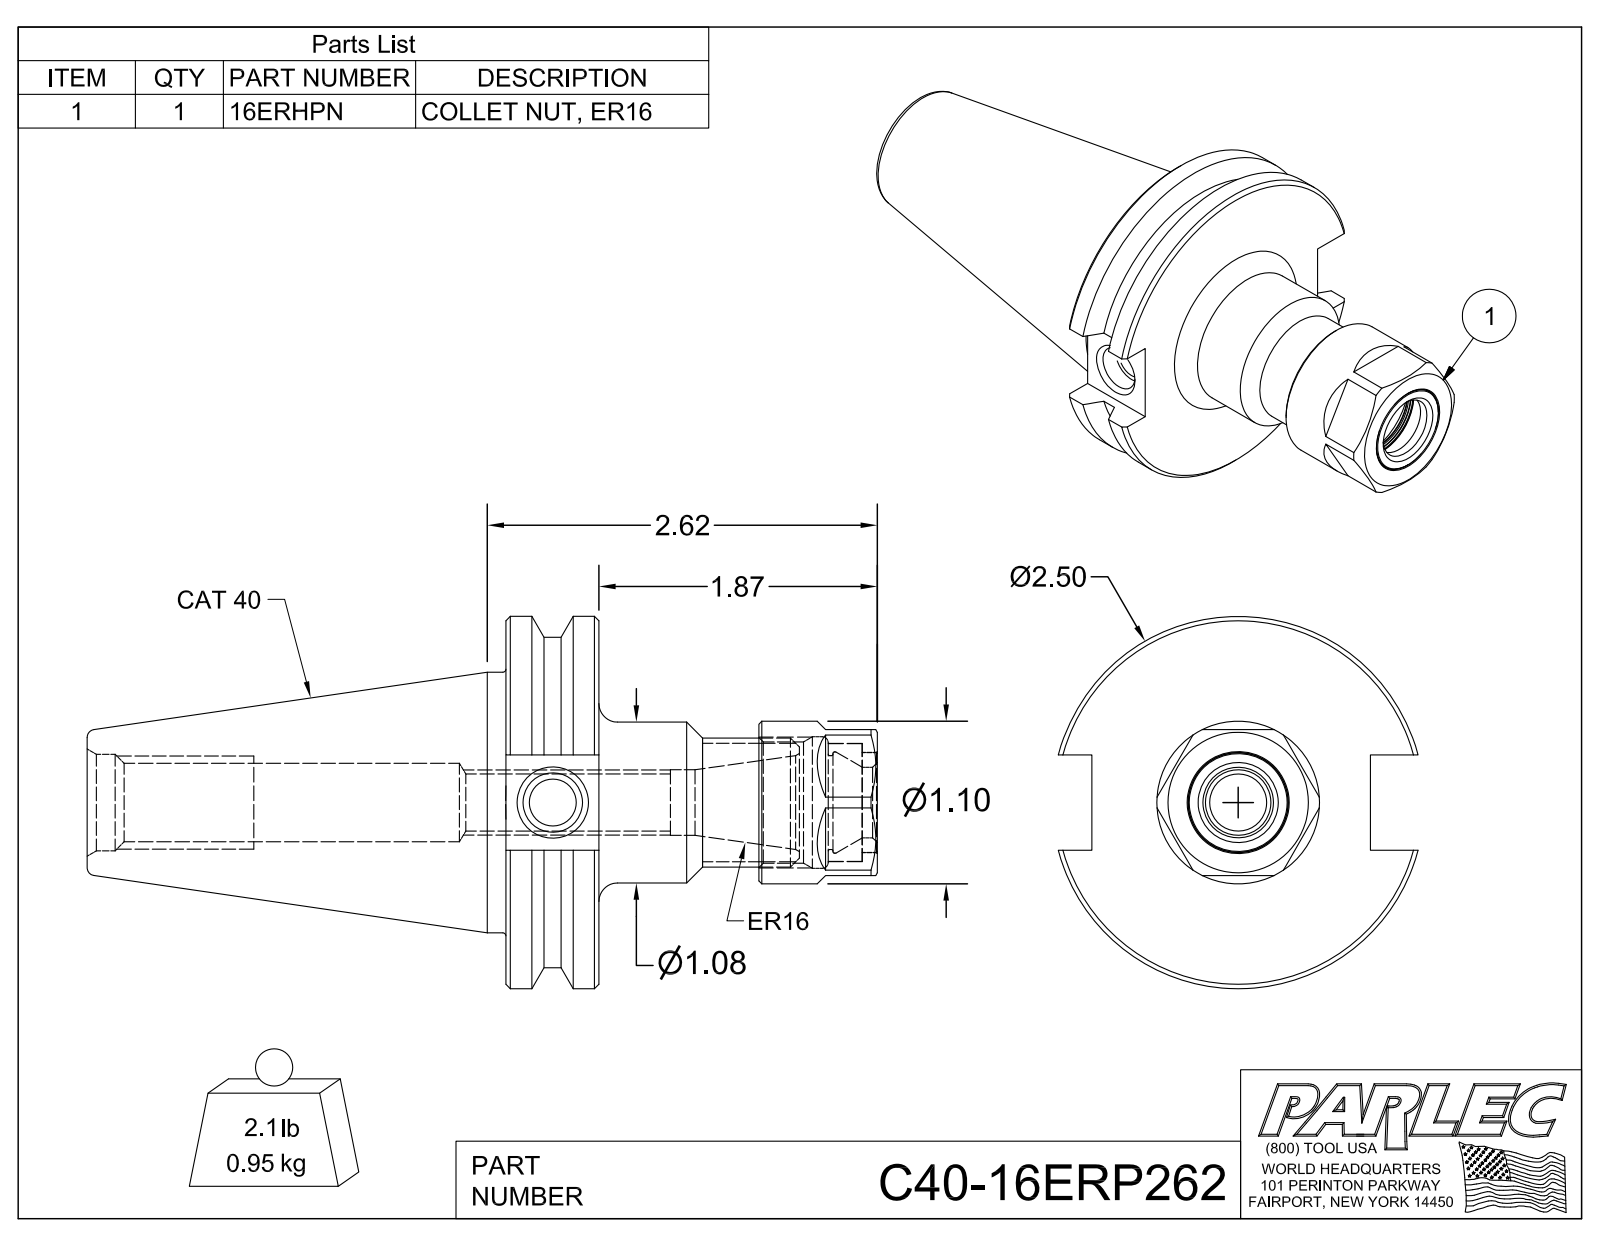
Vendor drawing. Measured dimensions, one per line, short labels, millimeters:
name: C40-16ER2-1; 16ERHPN; C40-16ERP262
written by: Autodesk Inventor 2016 (AUTOMOTIVE_DESIGN)
unit: mm
bodies: 3 solids, 89 faces (31 planar, 24 cylindrical, 34 other)
size: 134.81 × 63.5 × 61.38
volume: 120 619 mm³; area: 28 278 mm²
holes: 1× ⌀9.73, 1× ⌀11.18, 1× ⌀12.04, 1× ⌀13.39, 1× ⌀14.3, 1× ⌀16, 1× ⌀16.46, 1× ⌀17.11, 1× ⌀17.27, 1× ⌀20.17, 1× ⌀20.68, 1× ⌀22.43
bosses: 1× ⌀63.5, 1× ⌀56.36, 1× ⌀44.45, 1× ⌀27.74, 1× ⌀27.43, 1× ⌀22, 1× ⌀20.07, 1× ⌀17.01
face distances: 15.88, 24.9, 63.38, 47.5, 4.32, 20.58, 16.26, 43.16, 27.28, 20.22
